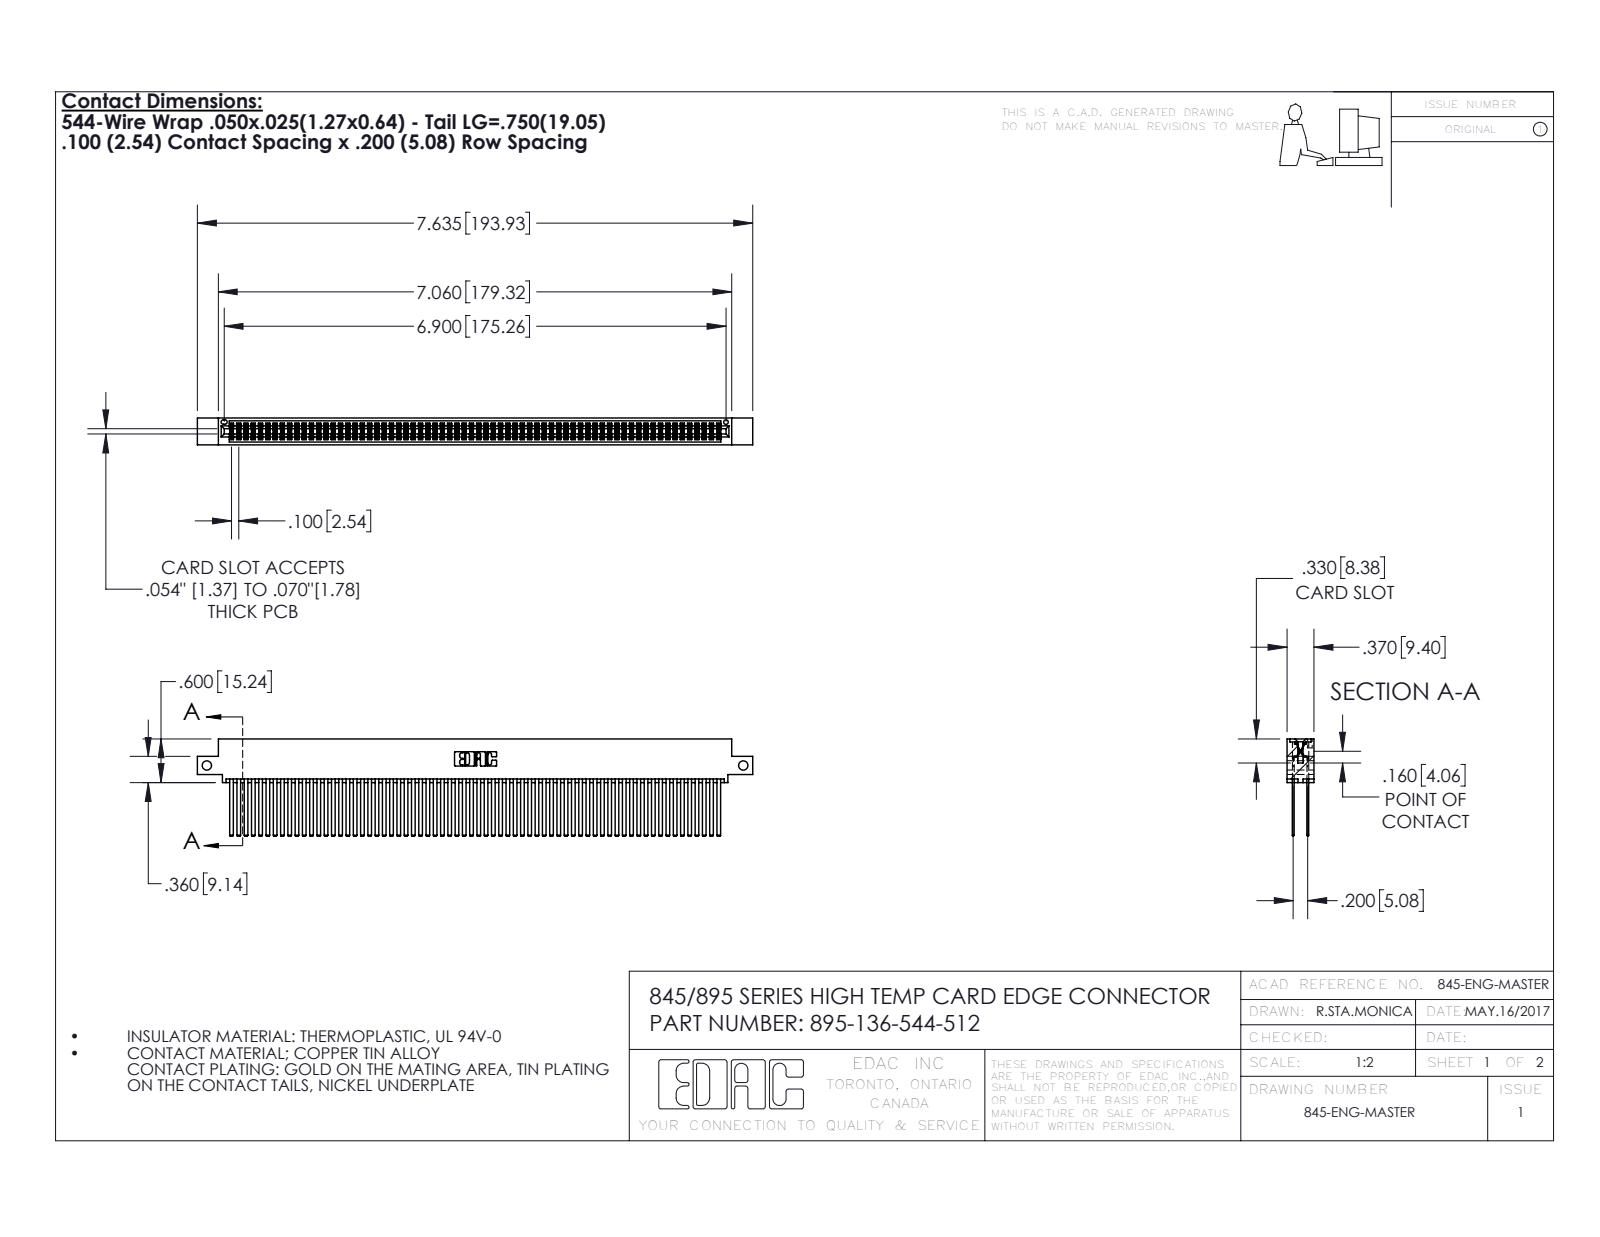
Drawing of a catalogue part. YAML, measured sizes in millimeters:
part_name: "345-292-001_345-293-144; 345 Part_0.110 Offset - Side Mount; 395-136-544-512"
step_written_by: "SolidWorks 2016 (CONFIG_CONTROL_DESIGN)"
units: millimeters
bodies: {solids: 137, faces: 6114, planar: 4028, cylindrical: 2086, other: 0}
overall_size: [193.9, 34, 9.4]
volume: 20830
surface_area: 36830
round_holes:
  - {diameter: 3.3, count: 2}
  - {diameter: 1.6, count: 1}
partial_cylinders:
  - {radius: 0.2, count: 204}
  - {radius: 0.3, count: 22}
  - {radius: 0.2, count: 6}
  - {radius: 0.8, count: 6}
  - {radius: 0.7, count: 3}
  - {radius: 0.4, count: 2}
  - {radius: 0.5, count: 2}
  - {radius: 0.6, count: 2}
face_to_face_distances: [5.1, 0.6, 7.6, 1.8, 2.5, 6.9, 5.7, 4.4, 9.4, 3.8]
hole_center_spacings: [187.3]
